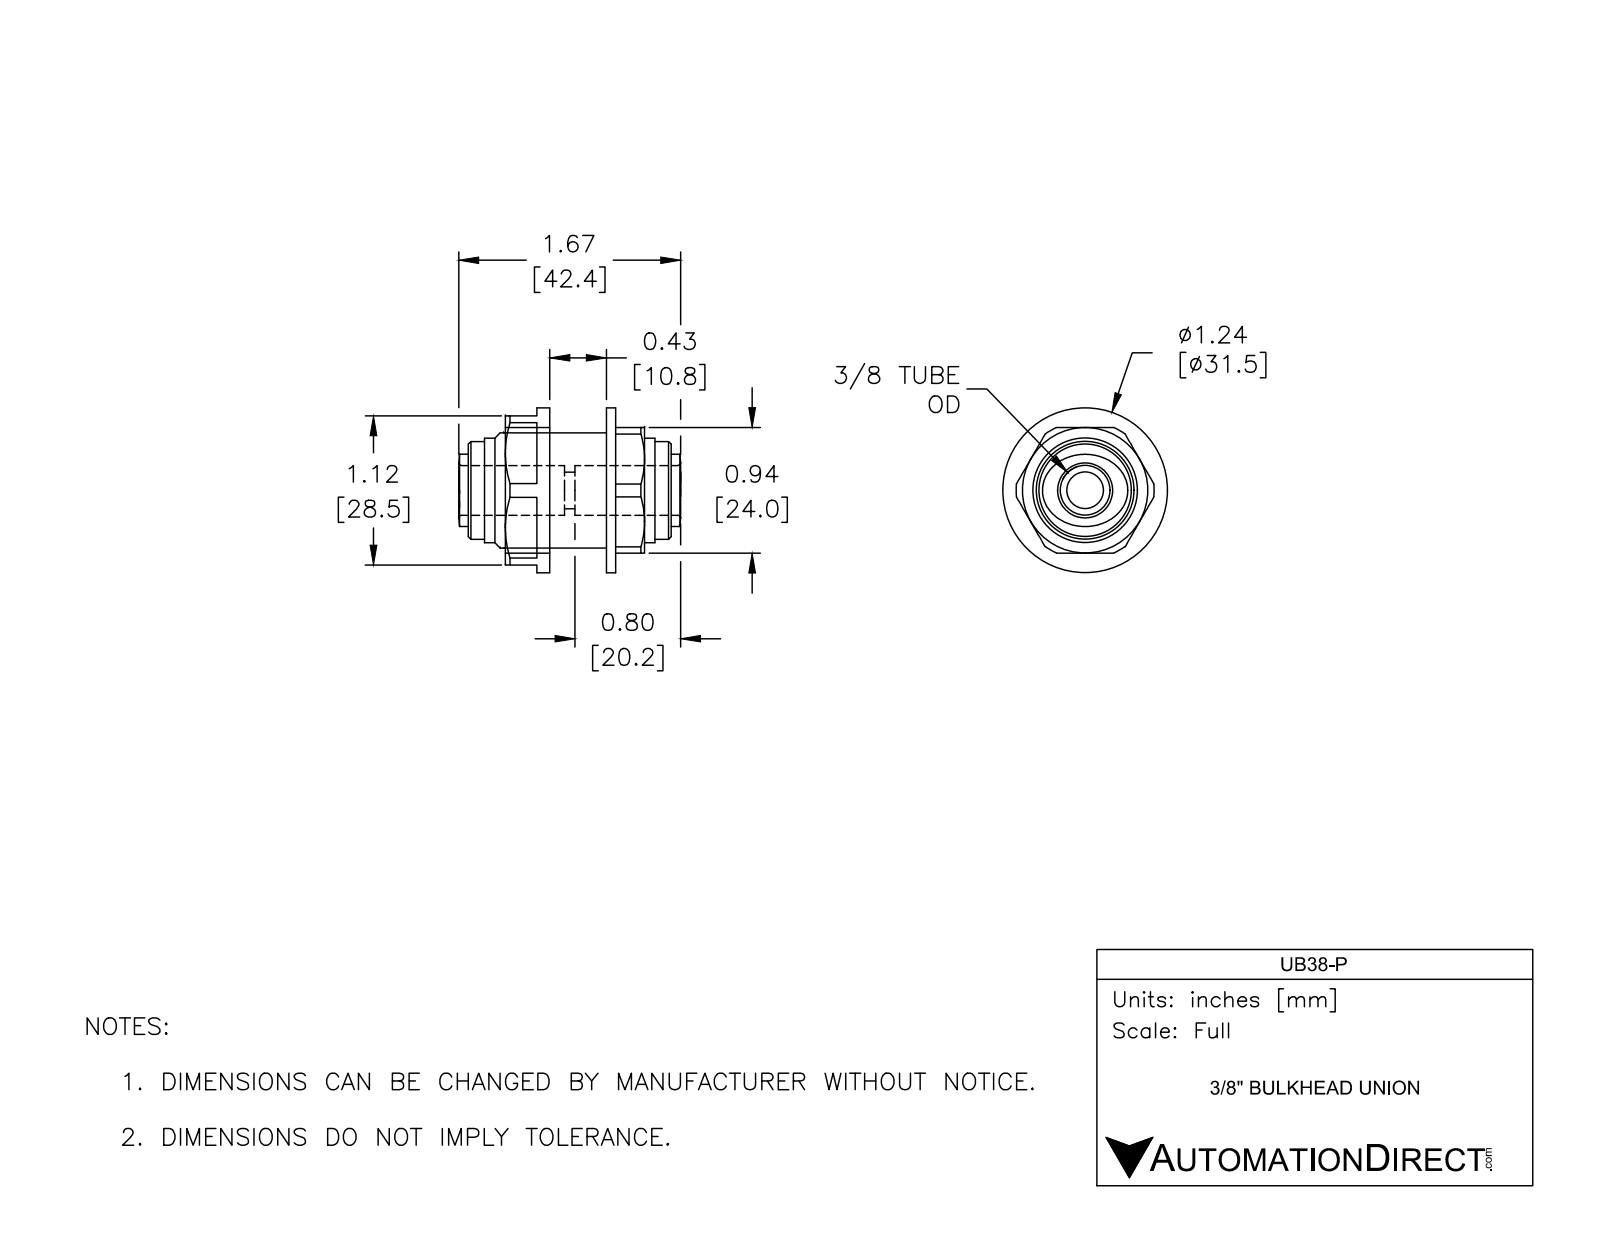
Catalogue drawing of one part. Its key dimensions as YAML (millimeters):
part_name: "UB38-P"
step_written_by: "SolidWorks 2017 (AUTOMOTIVE_DESIGN)"
units: millimeters
bodies: {solids: 1, faces: 93, planar: 31, cylindrical: 30, other: 32}
overall_size: [42.4, 31.5, 31.5]
volume: 16200
surface_area: 6716
round_holes:
  - {diameter: 7, count: 1}
  - {diameter: 9.5, count: 1}
round_bosses_or_shafts:
  - {diameter: 31.5, count: 1}
  - {diameter: 24, count: 1}
  - {diameter: 20, count: 1}
  - {diameter: 18.7, count: 1}
partial_cylinders:
  - {radius: 13.2, count: 1}
face_to_face_distances: [26.2, 2.3, 10.8, 1.8, 12.6, 28.5, 22, 21.1, 19.3, 8.5]
